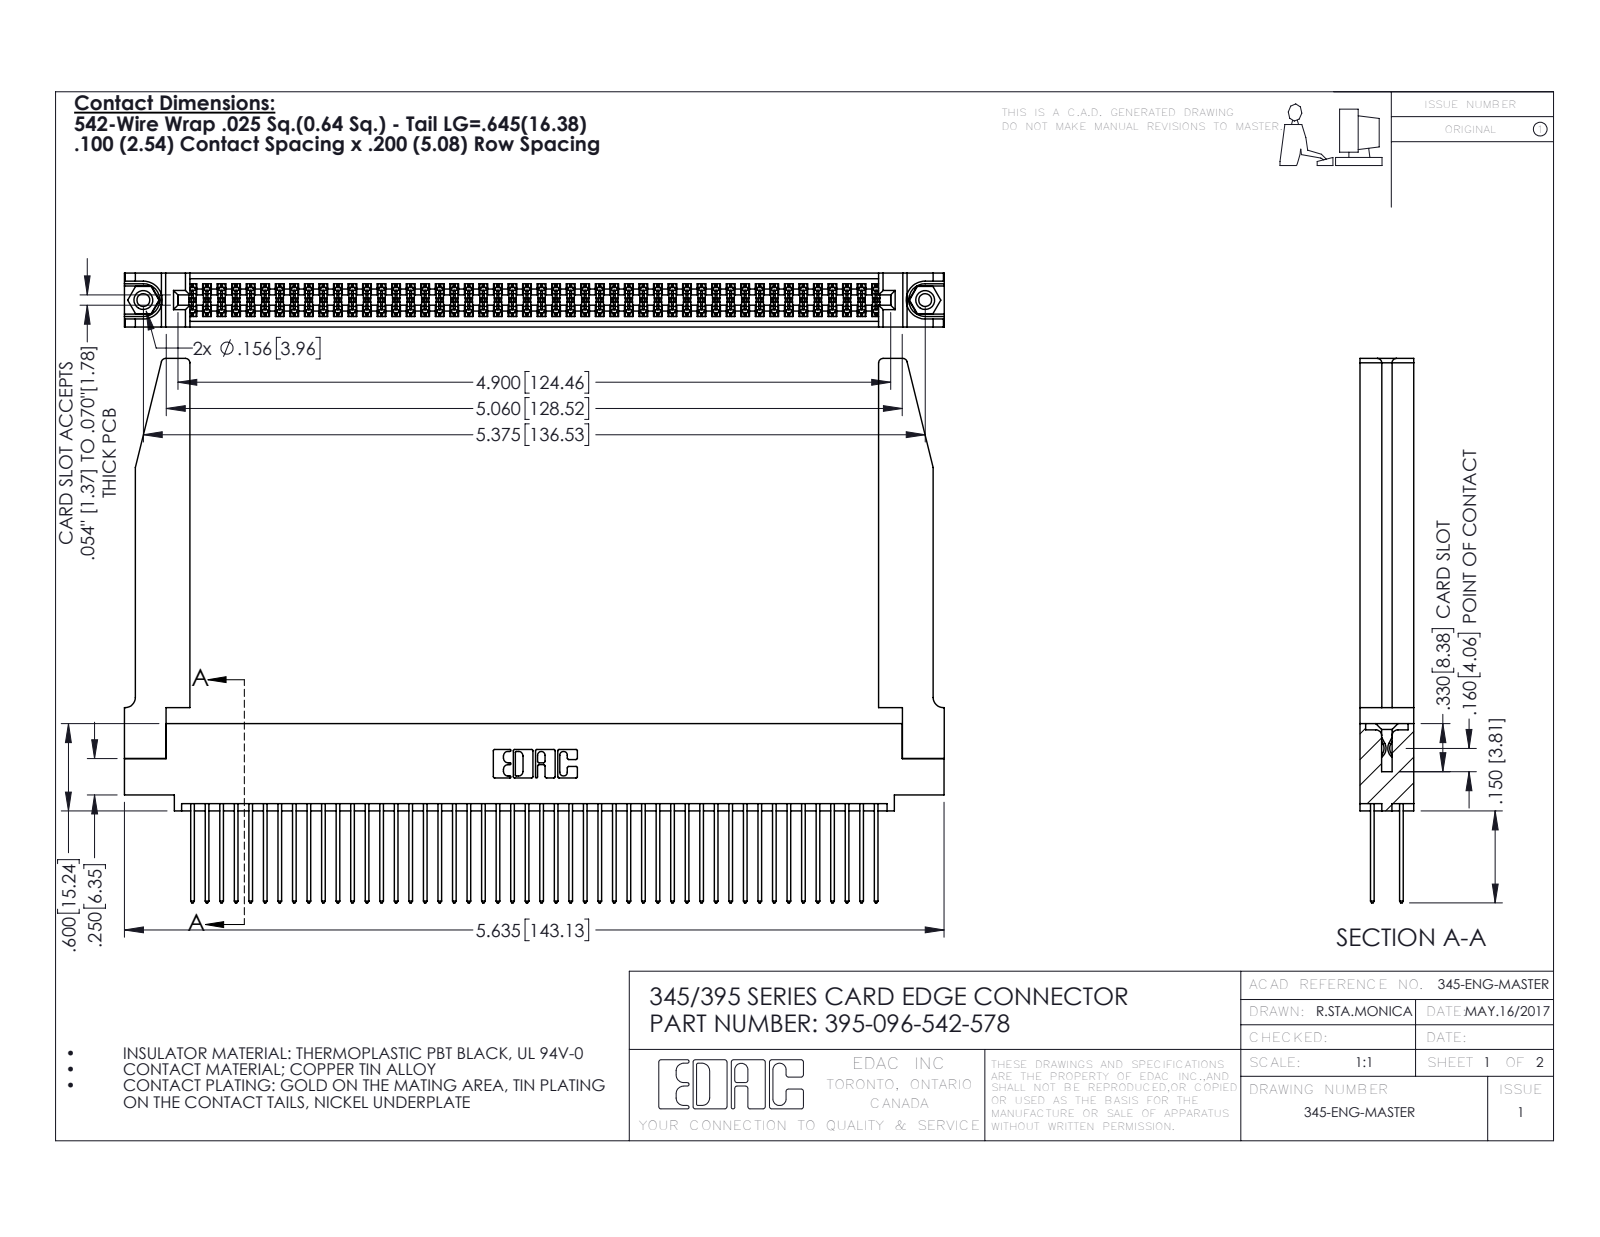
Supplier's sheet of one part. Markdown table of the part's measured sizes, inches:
| quantity | value |
| --- | --- |
| part name | 345-220-078_345-220-078; 345-292-001_345-293-142; 345-250-001_345-250-001-102; 345 Part_0.110 Offset - 0.156 Dia-TH (+1 more) |
| STEP written by | SolidWorks 2016 (CONFIG_CONTROL_DESIGN) |
| units | inches |
| bodies | 101 solids, 5164 faces (3394 planar, 1718 cylindrical, 52 other) |
| overall size | 5.636 × 3.742 × 0.37 |
| volume | 1.349 in³ |
| surface area | 47.01 in² |
| round holes (diameter × count) | 0.089 × 2, 0.125 × 2, 0.156 × 2, 0.064 × 1 |
| round bosses / shafts (diameter × count) | 0.155 × 2 |
| partial cylindrical surfaces (radius × count) | 0.006 × 144, 0.01 × 96, 0.01 × 22, 0.03 × 8, 0.007 × 6, 0.031 × 6, 0.026 × 3, 0.014 × 2 |
| main face-to-face distances | 0.072, 0.298, 0.37, 0.098, 0.272, 0.025, 0.2, 0.225, 0.175, 0.15 |
| hole center spacings | 0.27, 5.139, 5.375 |
